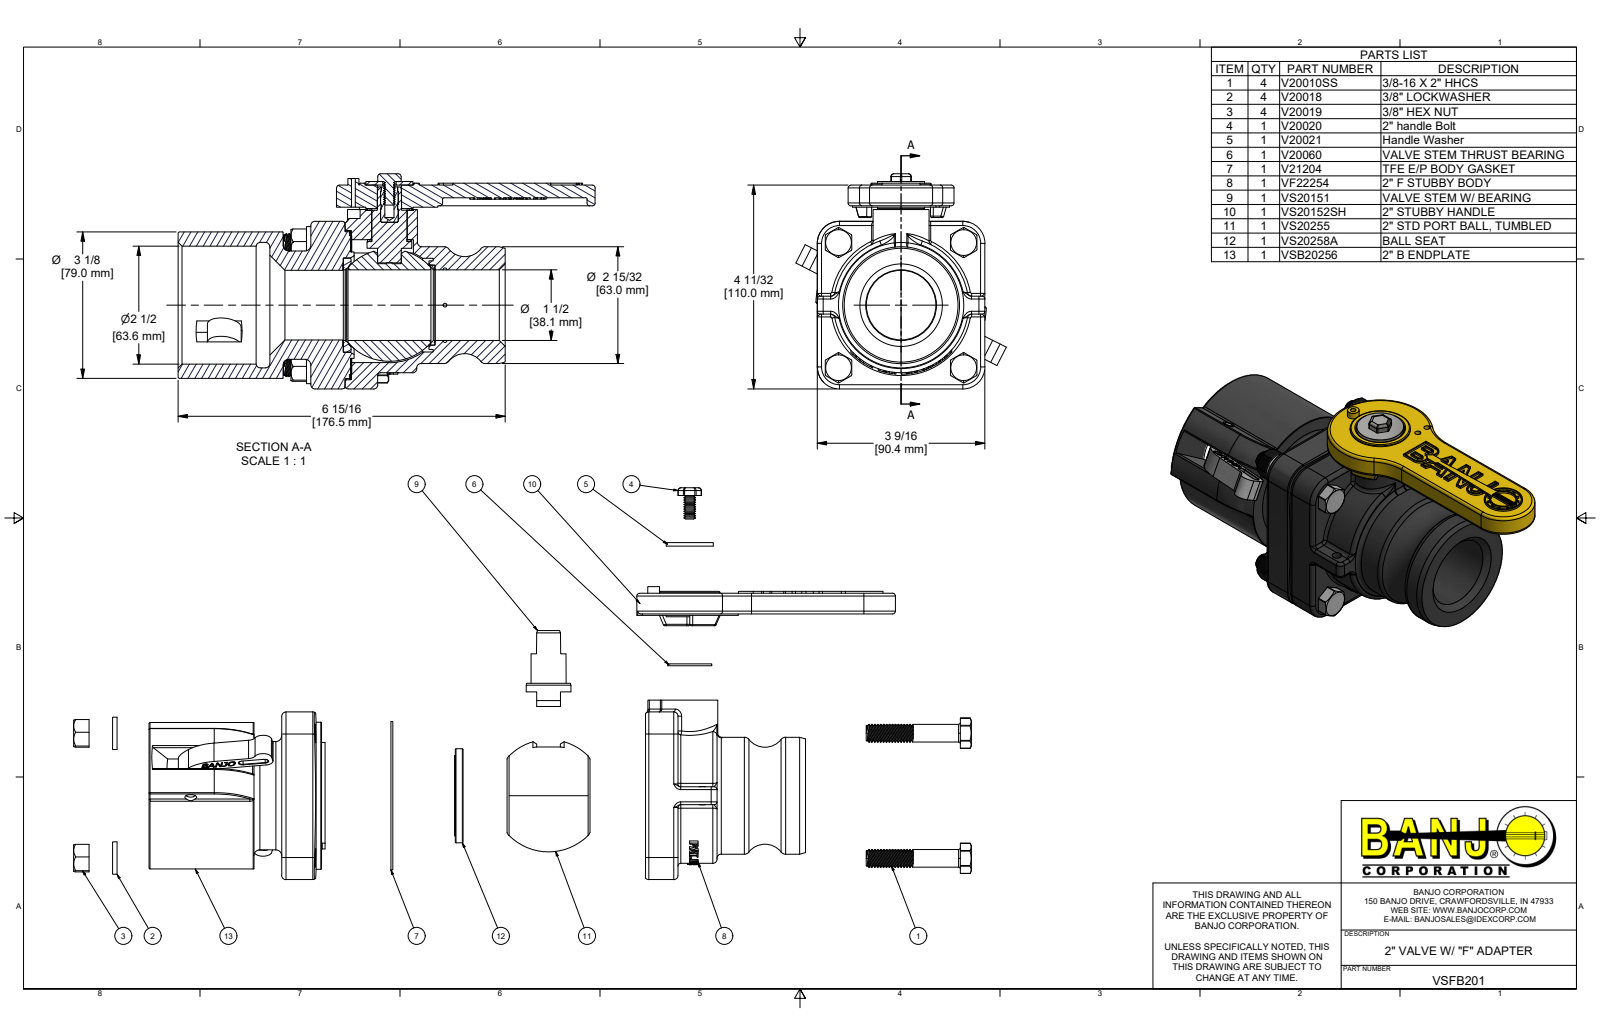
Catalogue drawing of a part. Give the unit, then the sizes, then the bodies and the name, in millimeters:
Units: millimetres
Overall size (bounding box): 225 × 116.1 × 113.6
Round holes (diameter × count): ⌀10.3 ×8, ⌀9.5 ×5, ⌀7.8 ×4, ⌀9.8 ×4, ⌀2 ×2, ⌀3.3 ×2, ⌀5.1 ×2, ⌀6.4 ×2, ⌀6.6 ×2, ⌀3 ×1, ⌀5 ×1, ⌀7.1 ×1
Round bosses / shafts (diameter × count): ⌀8.2 ×60, ⌀17.4 ×4, ⌀9.5 ×4, ⌀6.6 ×2, ⌀6.3 ×2, ⌀80 ×1, ⌀79.3 ×1, ⌀63 ×1
Partial cylindrical surfaces — rounded edges, fillets, slot ends (radius × count): R1.5 ×30, R0.8 ×23, R2.3 ×21, R4.1 ×8, R3.2 ×7, R4.6 ×6, R1.9 ×4, R8.1 ×4
Main face-to-face distances: 90.4, 21.5, 14.6, 17.5, 6.9, 36.1, 12.7, 18.5, 2.9, 1
Hole centre spacings: 47.8, 47.5, 67.3, 67.5, 40.5, 46.1, 67.4, 67.4
Volume: 608 800 mm³ · Surface area: 182 400 mm²
Bodies: 29 solids, 3104 faces (1251 planar, 678 cylindrical, 1175 other)
Part name (STEP PRODUCT): VSFB201; VF22254; VF22254Y; VF22254X (+8 more)
STEP written by: Autodesk Inventor 2019 (AUTOMOTIVE_DESIGN)
